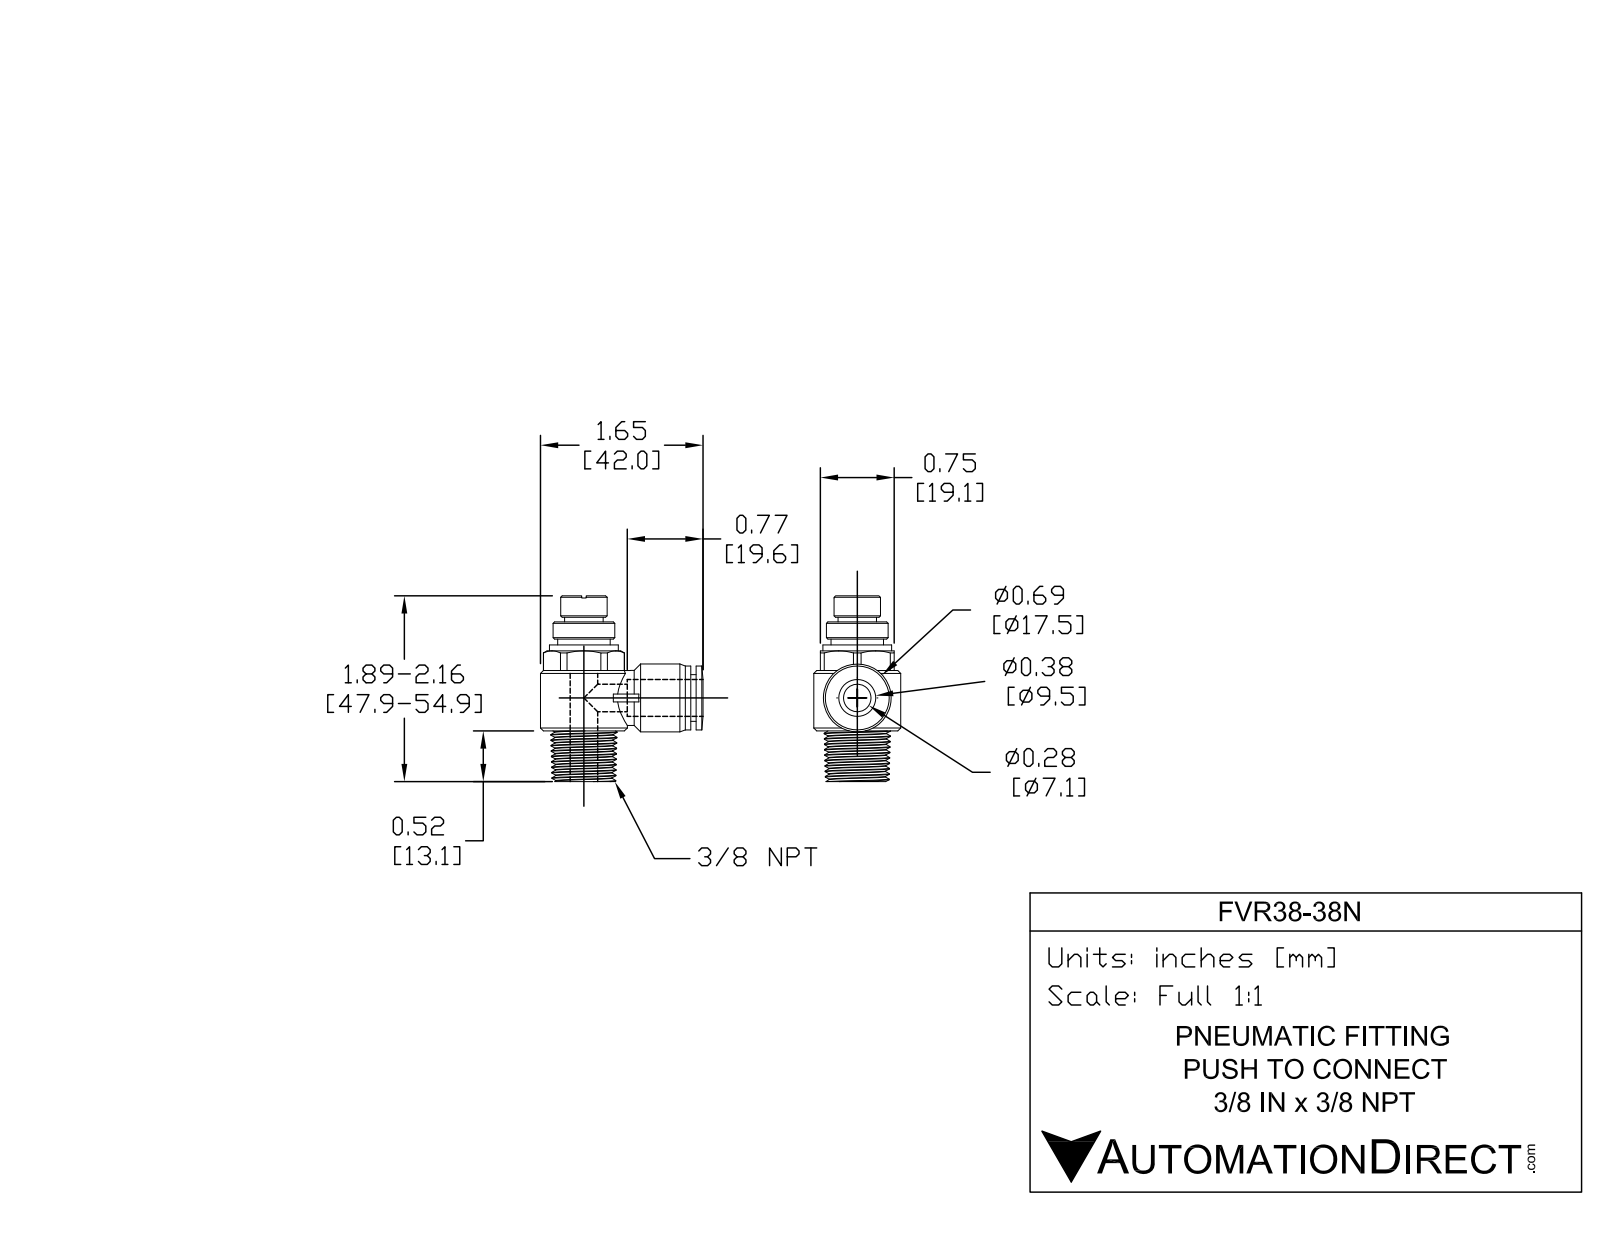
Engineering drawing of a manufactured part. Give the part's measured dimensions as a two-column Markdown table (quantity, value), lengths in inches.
| quantity | value |
| --- | --- |
| part name | FVR38-38N |
| STEP written by | SolidWorks 2015 (AUTOMOTIVE_DESIGN) |
| units | inches |
| bodies | 1 solid, 558 faces (252 planar, 143 cylindrical, 163 other) |
| overall size | 2.161 × 1.652 × 0.886 |
| volume | 0.896 in³ |
| surface area | 9.978 in² |
| round holes (diameter × count) | 0.236 × 2, 0.386 × 1 |
| round bosses / shafts (diameter × count) | 0.886 × 1, 0.748 × 1, 0.689 × 1, 0.677 × 1, 0.669 × 1, 0.661 × 1, 0.591 × 1, 0.551 × 1 |
| partial cylindrical surfaces (radius × count) | 0.236 × 1, 0.315 × 1, 0.413 × 1 |
| main face-to-face distances | 0.748, 0.047, 0.228, 0.811, 1.039, 0.429, 0.555, 1.366, 1.594, 2.161 |
